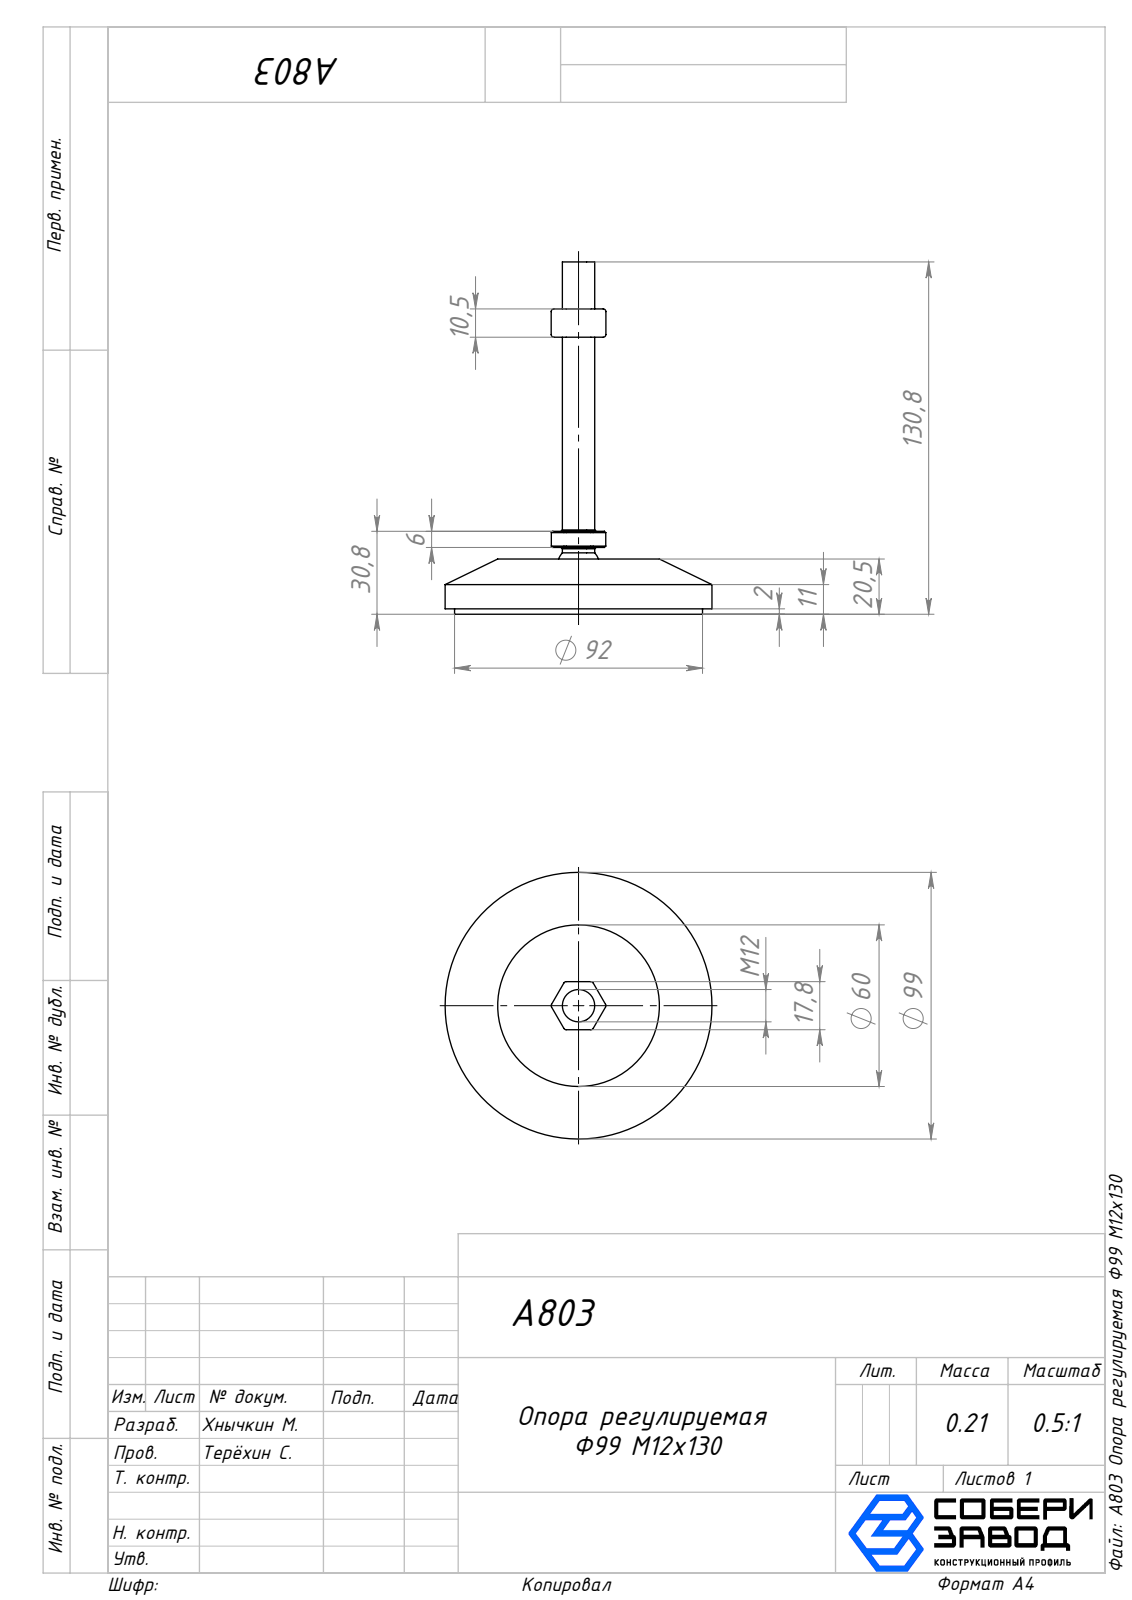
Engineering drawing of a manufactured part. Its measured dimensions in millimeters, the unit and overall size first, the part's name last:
Units: millimetres
Overall size (bounding box): 130.79 × 99 × 99
Round holes (diameter × count): ⌀10 ×1, ⌀16 ×1
Round bosses / shafts (diameter × count): ⌀99 ×1, ⌀92 ×1, ⌀12 ×1
Partial cylindrical surfaces — rounded edges, fillets, slot ends (radius × count): R1 ×24
Main face-to-face distances: 20.5, 2, 18.5, 17.8, 17.84, 17.76, 130.79, 128.79, 110.29, 30.79
Volume: 146 159 mm³ · Surface area: 26 204 mm²
Bodies: 3 solids, 110 faces (32 planar, 38 cylindrical, 40 other)
Part name (STEP PRODUCT): A803 Опора регулируемая Ф99 М12х130; Шарнирный вал M12_00; Опора_00; Гайка М12_00
STEP written by: SolidWorks 2025 (AUTOMOTIVE_DESIGN)
